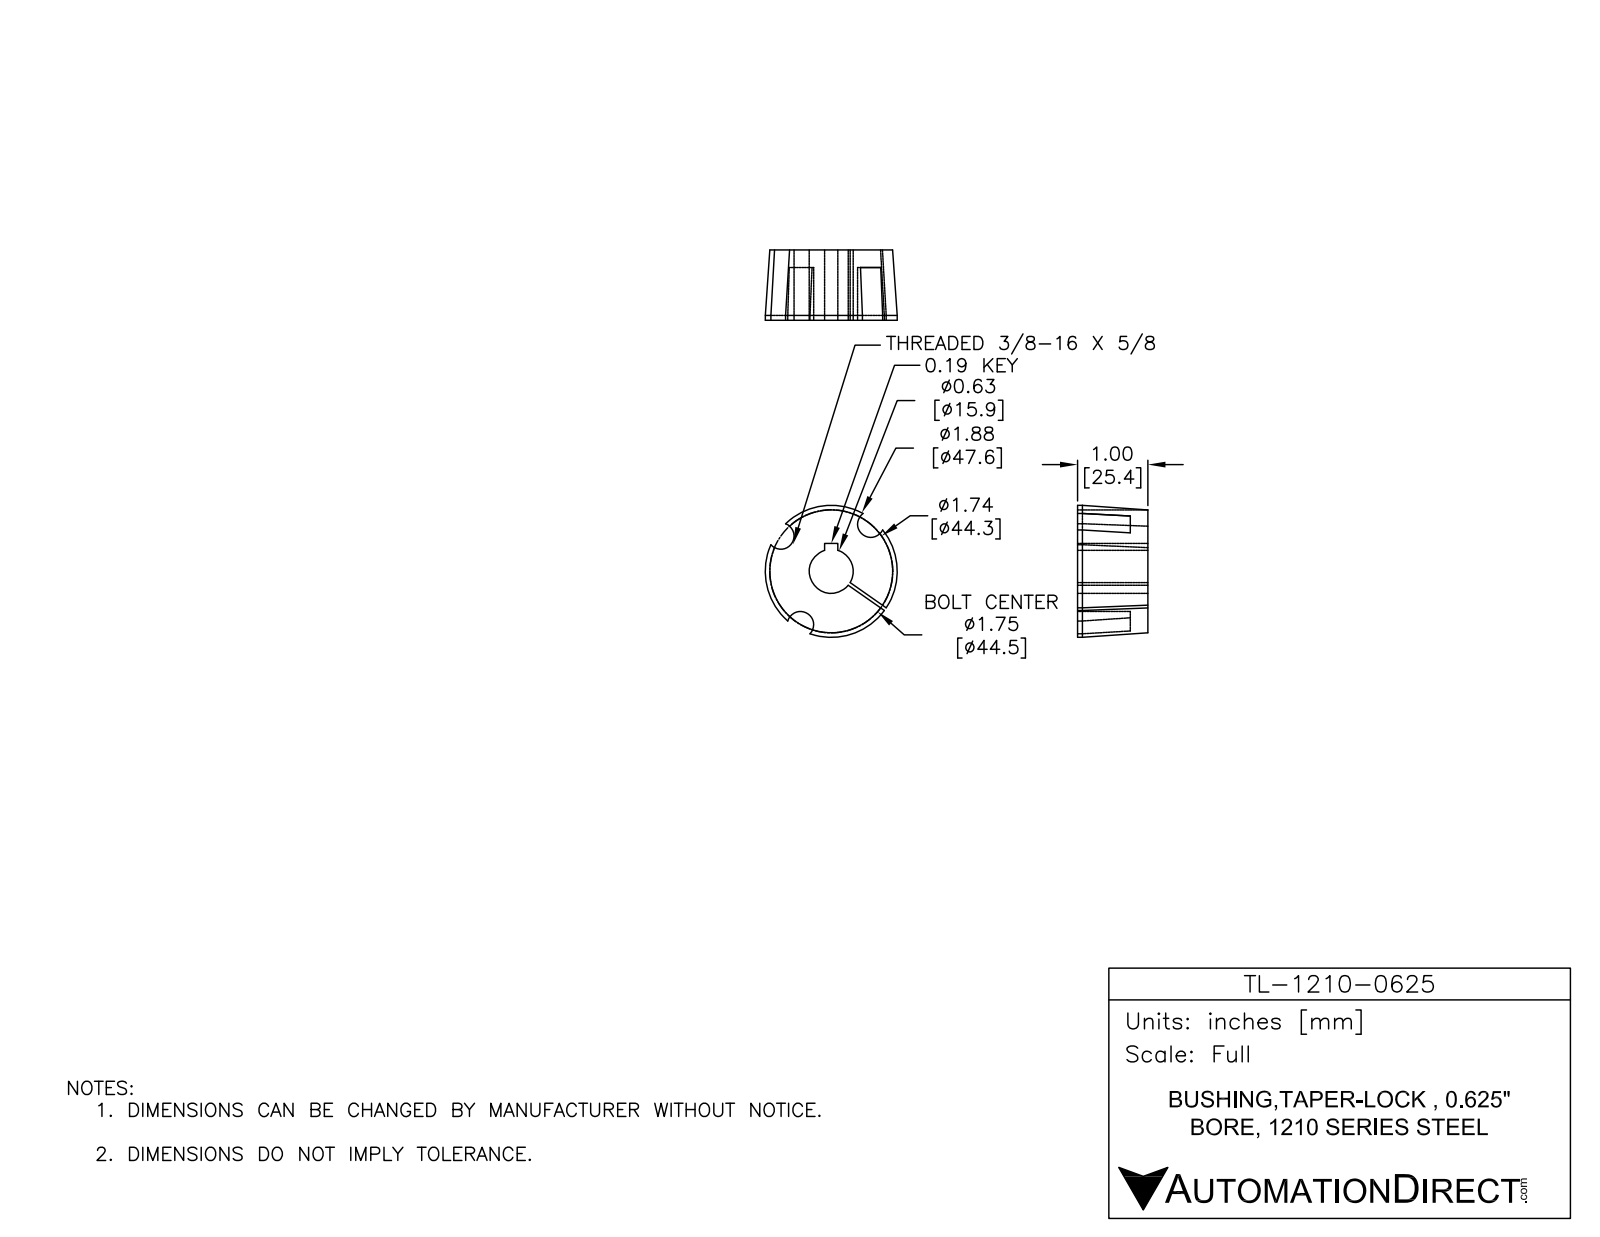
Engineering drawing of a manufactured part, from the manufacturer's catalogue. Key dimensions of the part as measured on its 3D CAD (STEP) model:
Part name (STEP PRODUCT): TL-1210-0625
STEP written by: SolidWorks 2014 (AUTOMOTIVE_DESIGN)
Units: inches
Bodies: 1 solid, 25 faces (9 planar, 13 cylindrical, 3 other)
Overall size (bounding box): 1.875 × 1.875 × 1
Volume: 2.07 in³ · Surface area: 13.87 in²
Round holes (diameter × count): ⌀0.625 ×1
Round bosses / shafts (diameter × count): ⌀1.875 ×1
Partial cylindrical surfaces — rounded edges, fillets, slot ends (radius × count): R0.188 ×3
Main face-to-face distances: 1, 0.048, 0.25, 0.75, 0.187
